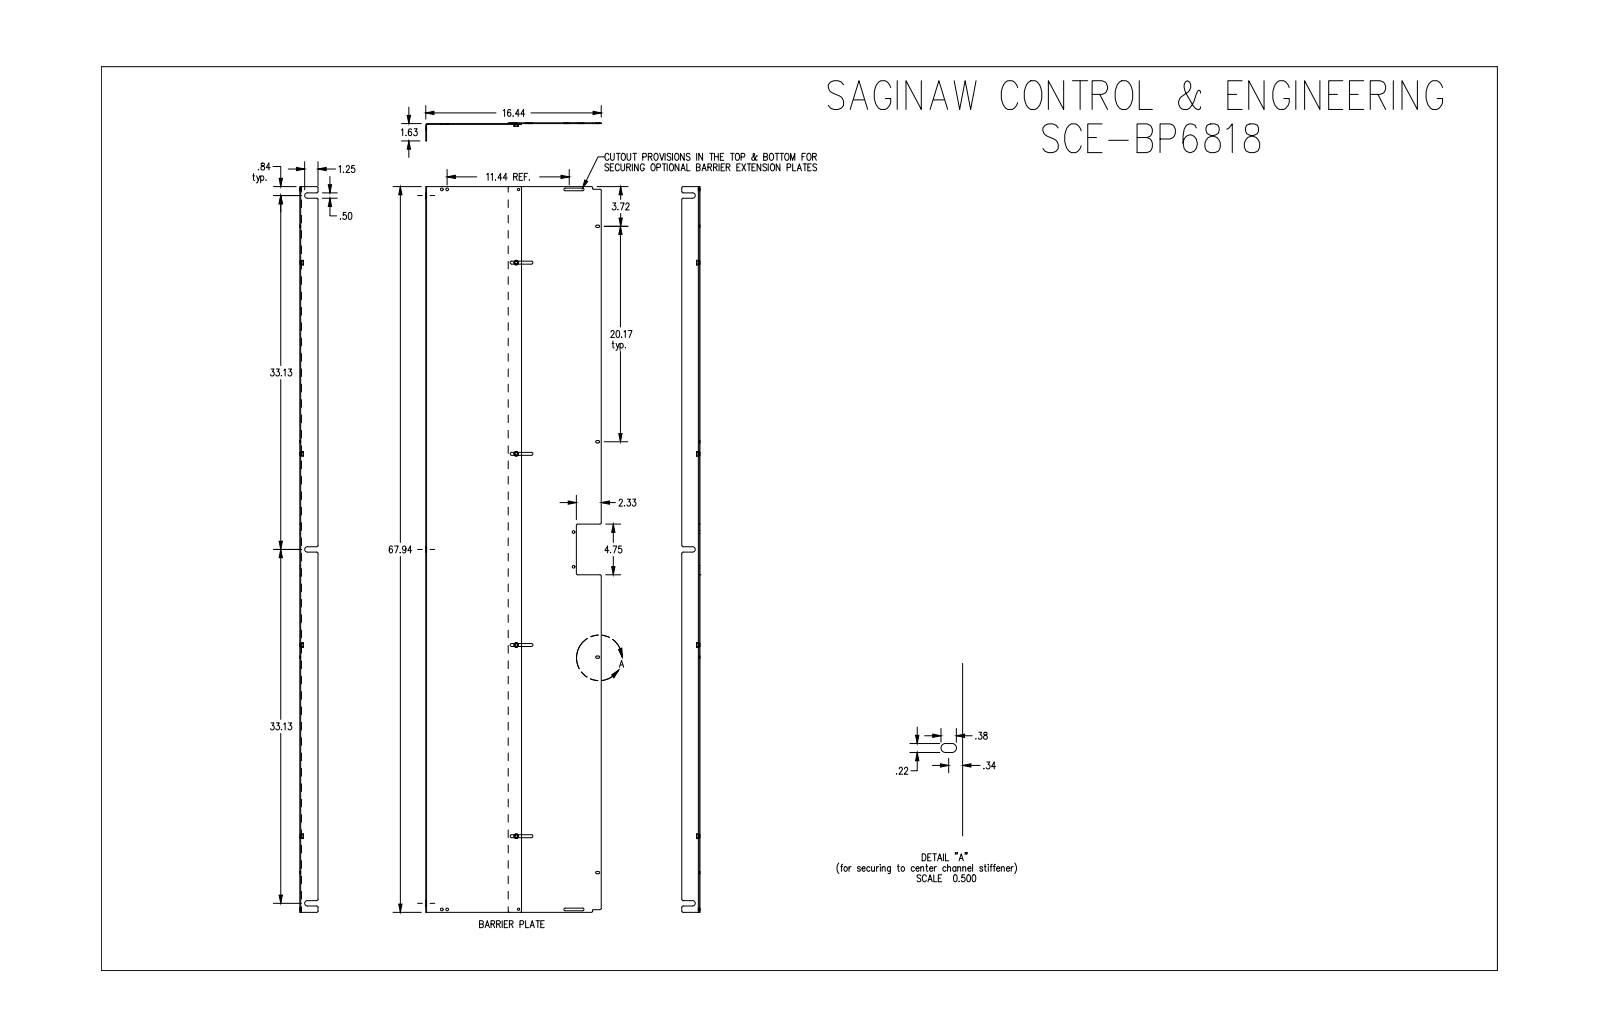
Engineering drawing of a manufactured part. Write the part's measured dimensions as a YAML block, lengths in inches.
part_name: "SCE-BP6818"
step_written_by: "SolidWorks 2019 (CONFIG_CONTROL_DESIGN)"
units: inches
bodies: {solids: 6, faces: 146, planar: 63, cylindrical: 71, other: 12}
overall_size: [67.937, 16.44, 1.7]
volume: 96.62
surface_area: 2604
round_holes:
  - {diameter: 0.25, count: 10}
  - {diameter: 0.344, count: 4}
  - {diameter: 0.218, count: 2}
round_bosses_or_shafts:
  - {diameter: 0.44, count: 4}
  - {diameter: 0.343, count: 4}
partial_cylinders:
  - {radius: 0.125, count: 24}
  - {radius: 0.109, count: 8}
  - {radius: 0.141, count: 8}
  - {radius: 0.25, count: 3}
  - {radius: 0.063, count: 2}
  - {radius: 0.042, count: 1}
  - {radius: 0.117, count: 1}
face_to_face_distances: [0.075, 0.15, 7.72, 7.645, 8.97, 8.895, 1.25, 1.7, 1.625, 1.55]
hole_center_spacings: [0.5, 6.689, 6.847, 7.189, 9.081, 9.426, 9.776, 11.858]
